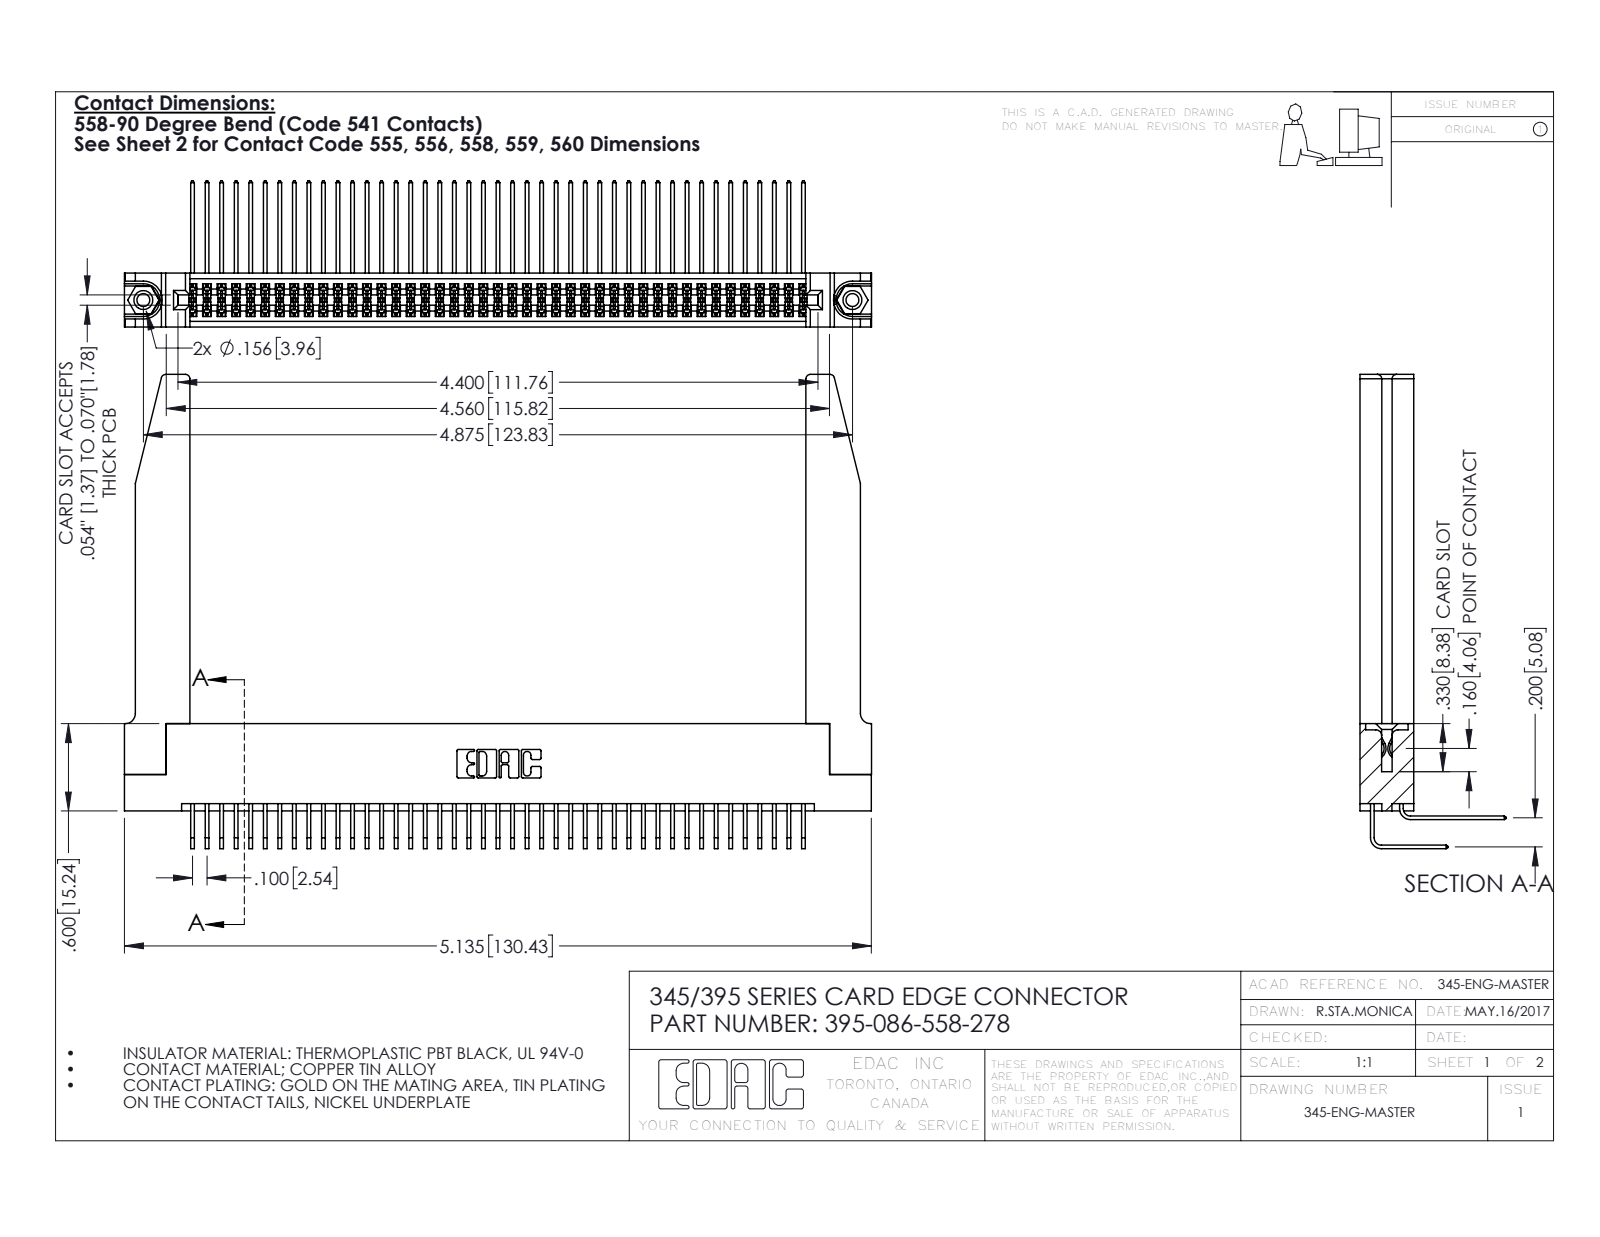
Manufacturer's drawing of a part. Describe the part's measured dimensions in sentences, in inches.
The part is named "395-086-558-278; 345 Part_Flush Mounting Lugs - 0.156 Dia-TH; 345-292-001_558 559 Tail - 1; 345-250-001_345-250-001-102 (+2 more)". Its 3-D file was written by "SolidWorks 2016 (CONFIG_CONTROL_DESIGN)". It is 91 solids with 4832 faces: 3232 planar, 1548 cylindrical and 52 other. Overall it measures 5.136 by 3.259 by 1.005 inches. Its volume is 1.278 cubic inches and its surface area 44.44 square inches. Round holes: 2 of diameter 0.089, 2 of diameter 0.125, 2 of diameter 0.156, 1 of diameter 0.064. Round bosses or shafts: 2 of diameter 0.155. Partial cylindrical surfaces (rounded edges, fillets, slot ends): 130 of radius 0.006, 22 of radius 0.01, 8 of radius 0.03, 6 of radius 0.007, 6 of radius 0.031, 3 of radius 0.026, 2 of radius 0.014, 2 of radius 0.019. The main face-to-face distances are 0.072, 0.37, 0.298, 0.2, 0.098, 0.272, 0.025, 0.225, 0.285, 0.148. The hole center spacings are 0.27, 4.639, 4.875.
